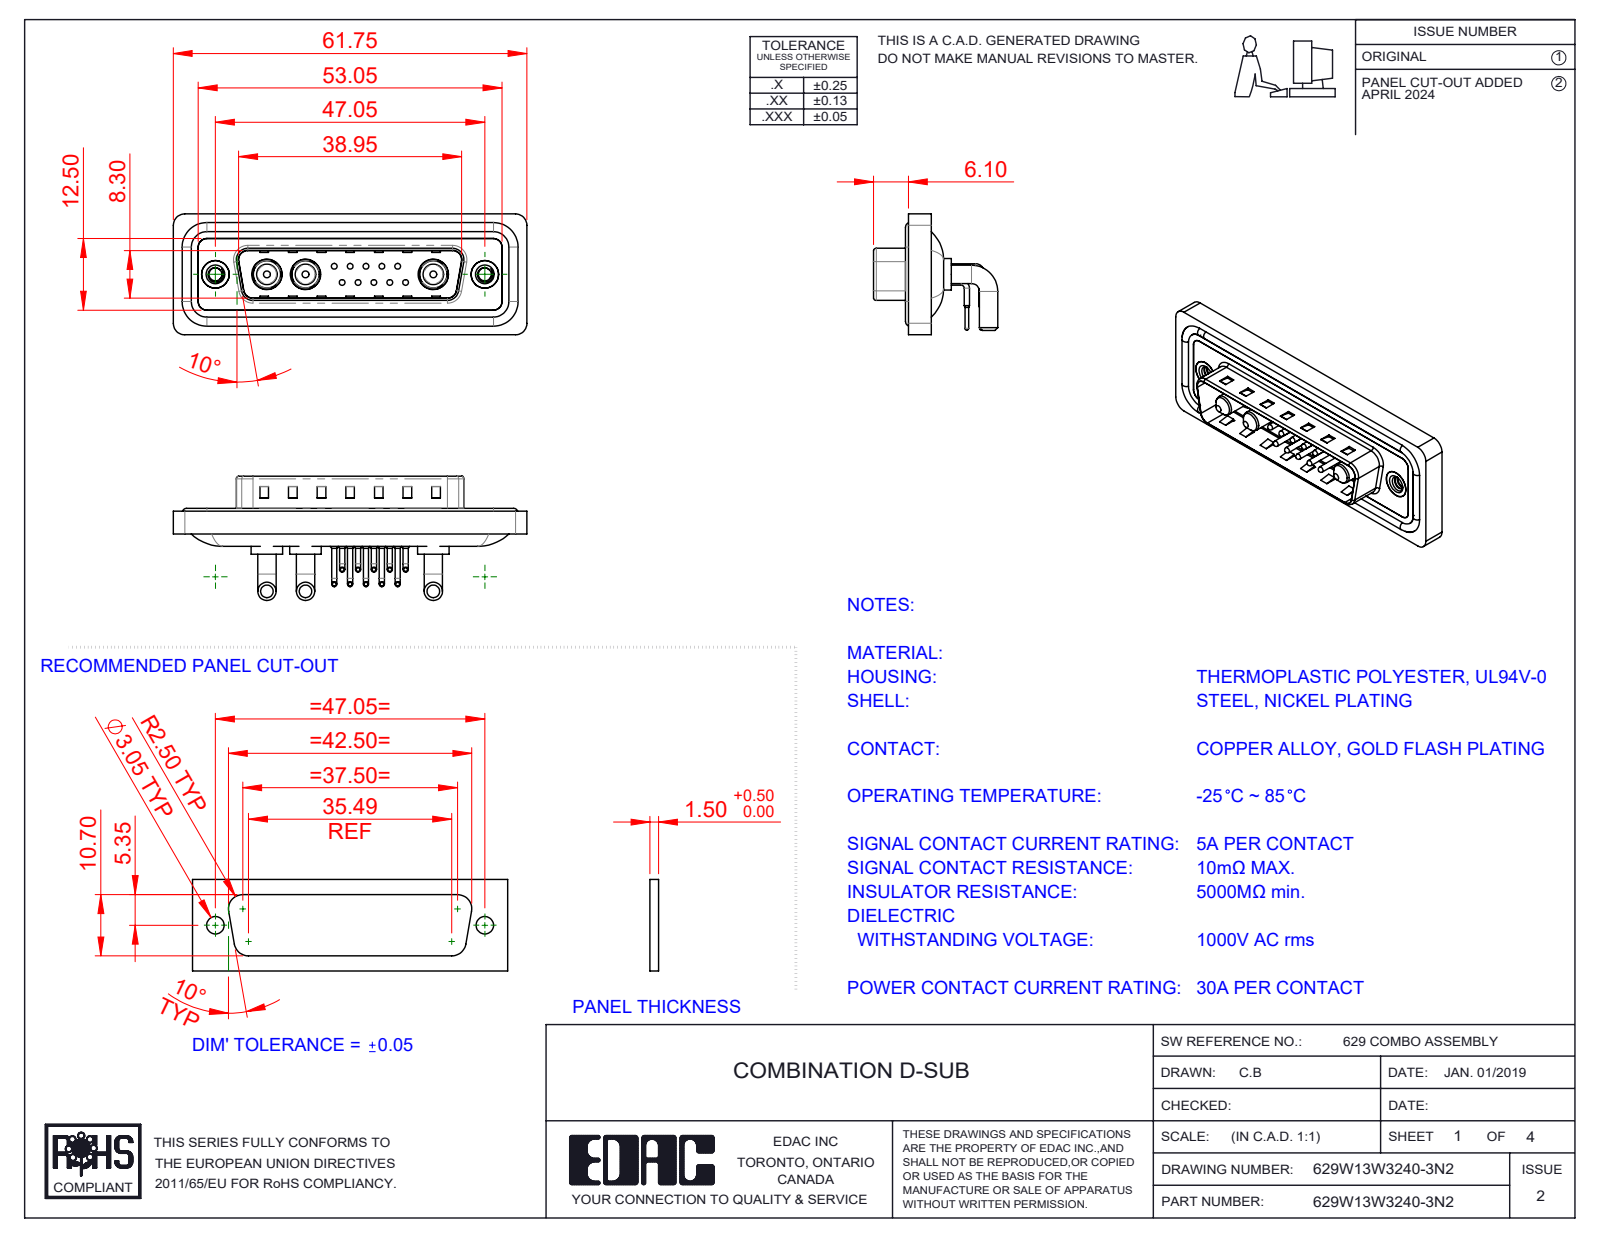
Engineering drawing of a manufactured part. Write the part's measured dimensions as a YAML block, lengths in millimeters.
part_name: "629W13W3140-3N2; 629Combo Shell Rear_25 Contacts; 629Combo Shell Front_25 Contacts; Power Pin_30A RA (+5 more)"
step_written_by: "SolidWorks 2023 (CONFIG_CONTROL_DESIGN)"
units: millimeters
bodies: {solids: 23, faces: 1712, planar: 879, cylindrical: 611, other: 222}
overall_size: [61.75, 21.7, 21.1]
volume: 7705
surface_area: 12552
round_holes:
  - {diameter: 0.75, count: 10}
  - {diameter: 1.6, count: 10}
  - {diameter: 2, count: 10}
  - {diameter: 4.85, count: 3}
  - {diameter: 5.3, count: 3}
  - {diameter: 2.26, count: 2}
  - {diameter: 4, count: 2}
  - {diameter: 4.8, count: 2}
  - {diameter: 5, count: 2}
round_bosses_or_shafts:
  - {diameter: 0.9, count: 20}
  - {diameter: 1.5, count: 10}
  - {diameter: 1, count: 10}
  - {diameter: 0.65, count: 10}
  - {diameter: 3.2, count: 6}
  - {diameter: 1.6, count: 4}
  - {diameter: 5.5, count: 3}
  - {diameter: 5.2, count: 3}
partial_cylinders:
  - {radius: 1.5, count: 18}
  - {radius: 2, count: 18}
  - {radius: 1.01, count: 10}
  - {radius: 0.5, count: 8}
  - {radius: 1.6, count: 8}
  - {radius: 0.25, count: 4}
  - {radius: 0.6, count: 4}
  - {radius: 0.65, count: 4}
face_to_face_distances: [0.4, 2.9, 0.8, 4.1, 1.1, 2.1, 1.6, 4.5, 1.5, 2.5]
hole_center_spacings: [3.16, 2.77, 5.04, 5.54, 7.49, 5.03, 8.31, 10.11]
